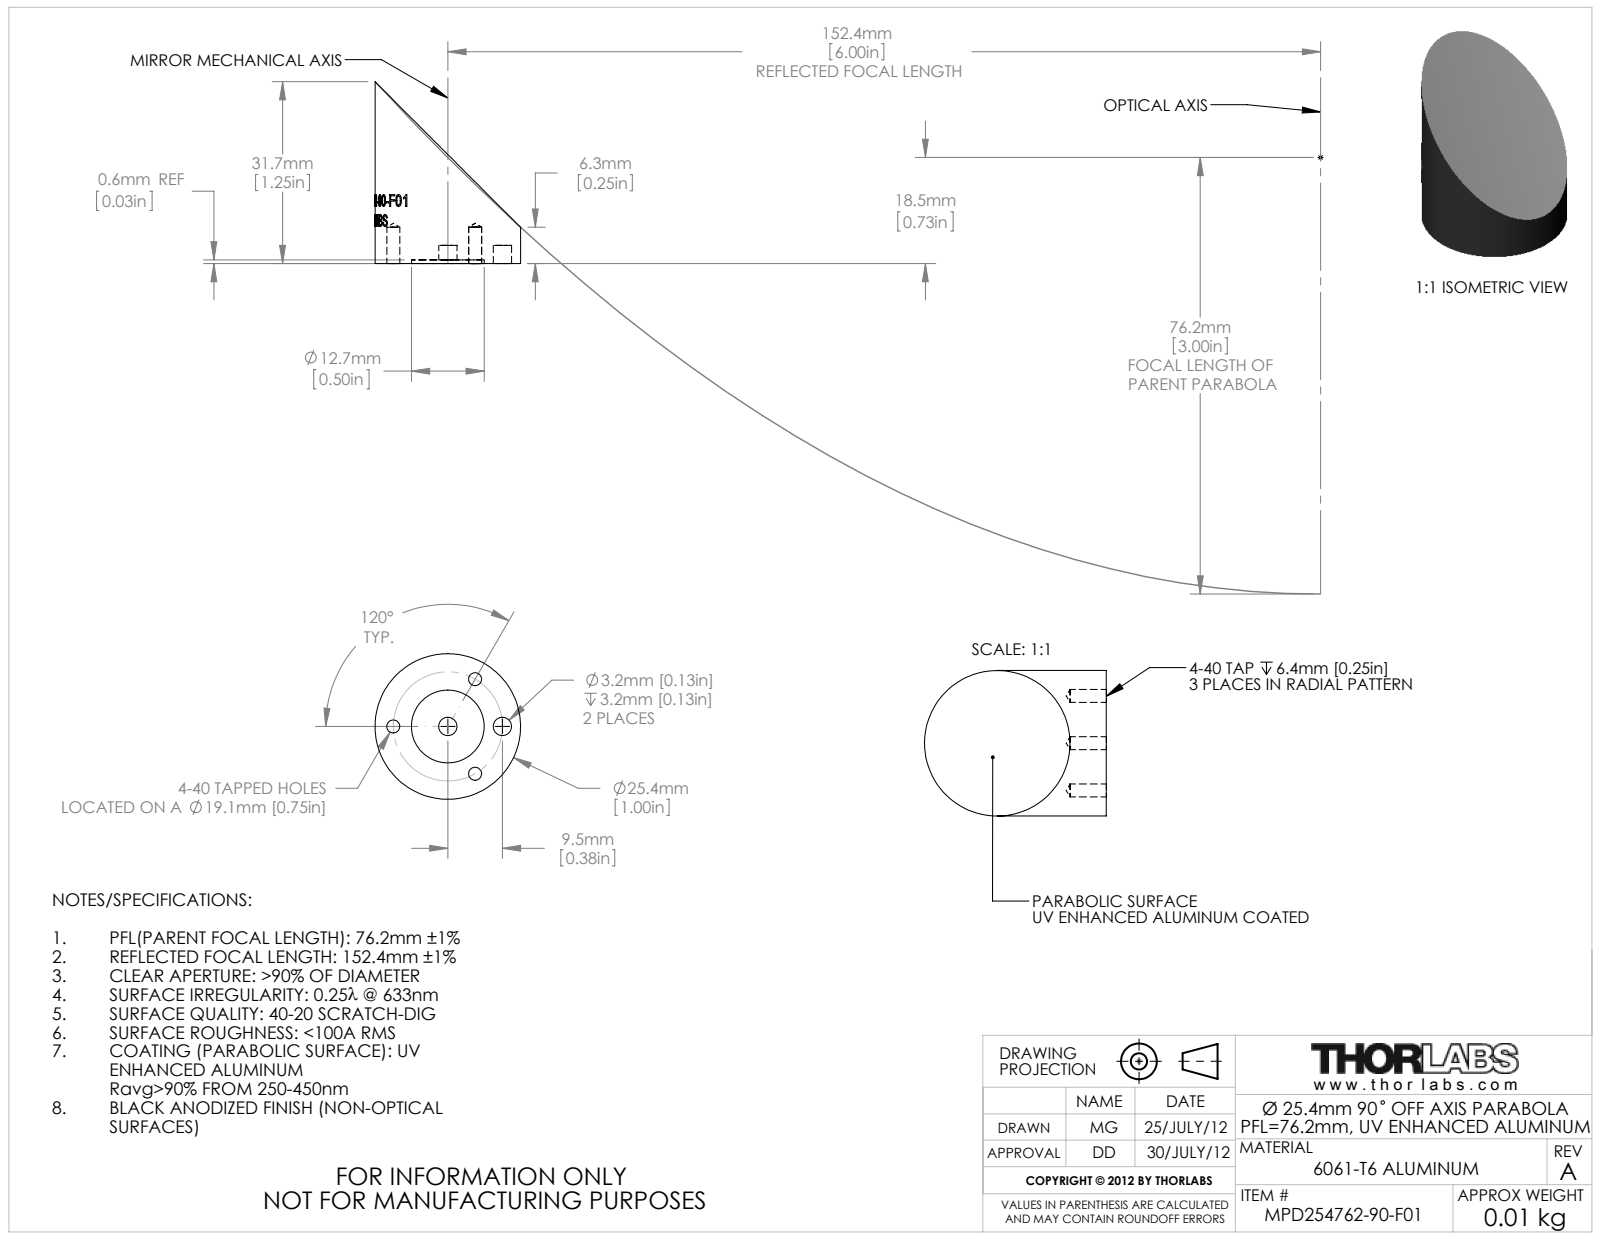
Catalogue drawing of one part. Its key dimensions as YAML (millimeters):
part_name: "24690-E0W"
step_written_by: "SolidWorks 2012 (CONFIG_CONTROL_DESIGN)"
units: millimeters
bodies: {solids: 1, faces: 62, planar: 4, cylindrical: 50, other: 8}
overall_size: [31.75, 25.4, 25.4]
volume: 9313
surface_area: 2964
round_holes:
  - {diameter: 2.26, count: 3}
  - {diameter: 3.19, count: 2}
  - {diameter: 12.7, count: 1}
round_bosses_or_shafts:
  - {diameter: 25.4, count: 1}
face_to_face_distances: [0.64, 3.17, 2.53]
hole_center_spacings: [9.52, 16.5, 9.53, 19.05]
